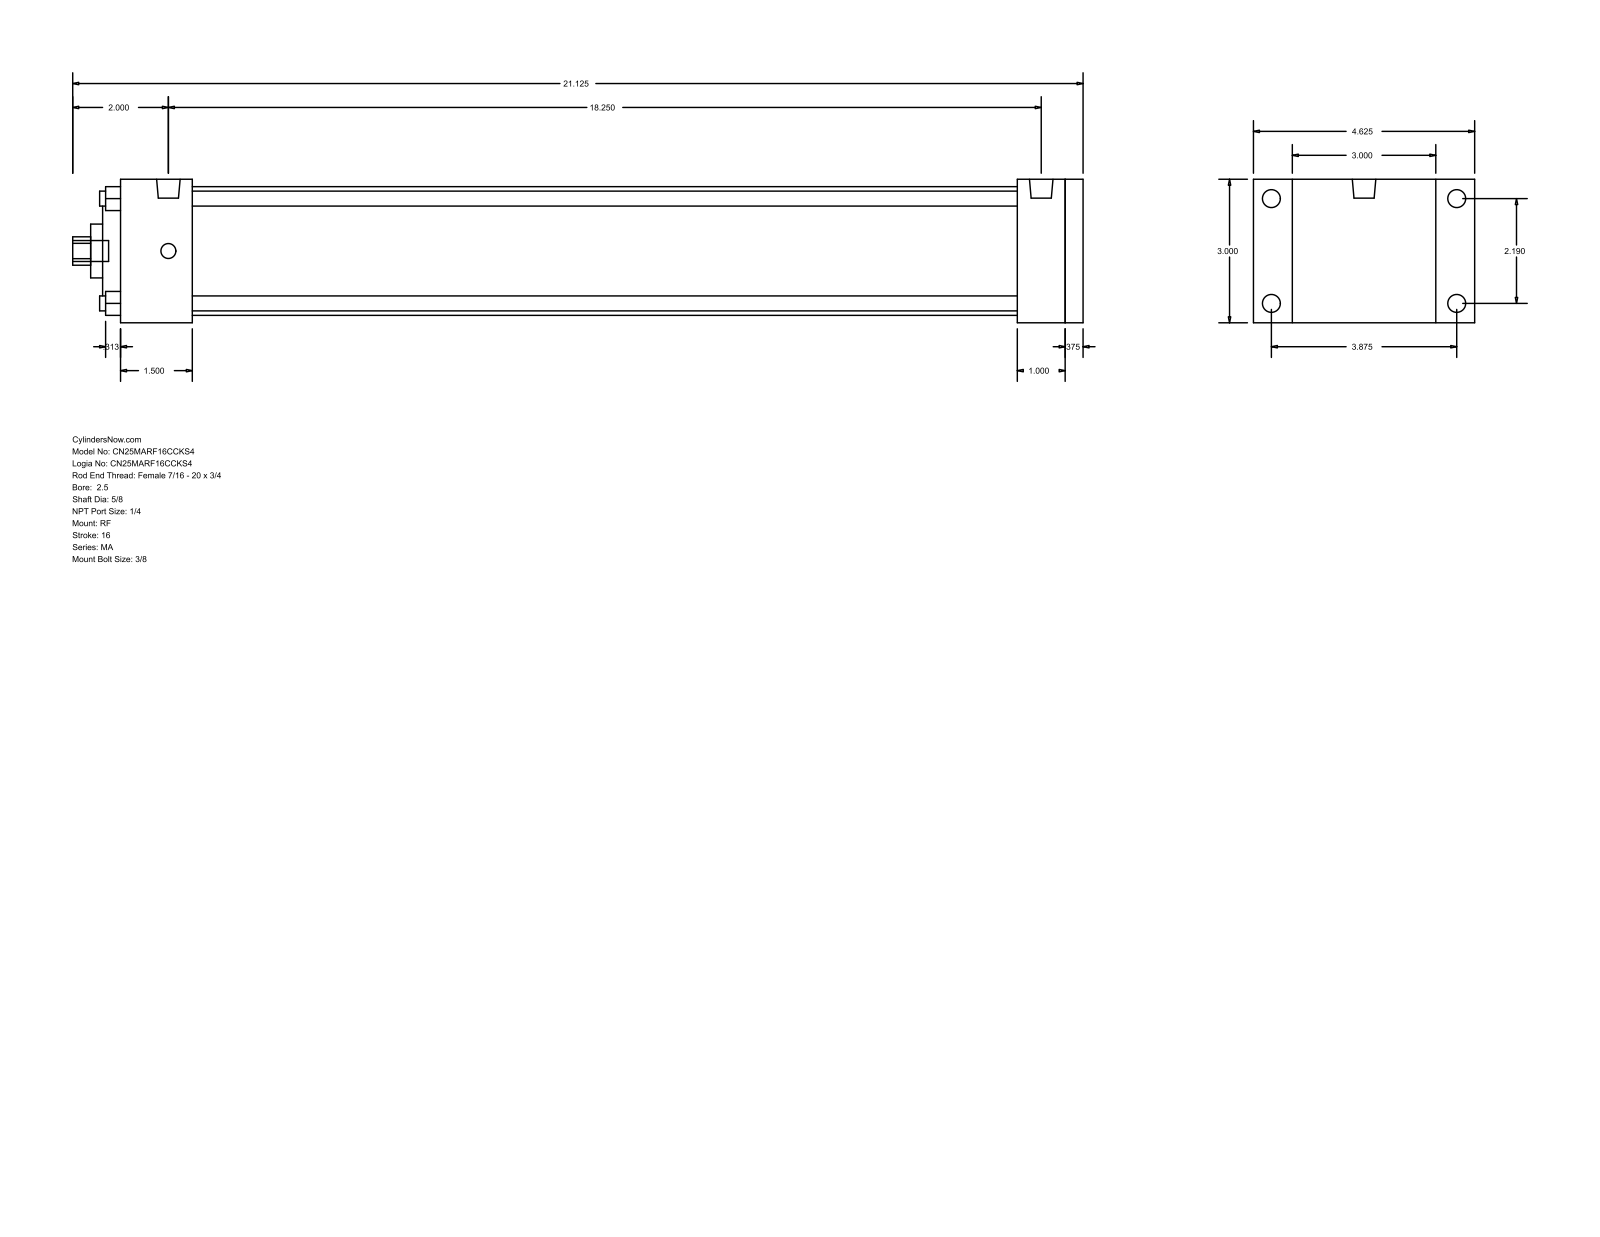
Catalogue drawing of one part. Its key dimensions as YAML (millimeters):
part_name: "MA_RF__0250_0.625"
step_written_by: "GSSL Pune (CONFIG_CONTROL_DESIGN)"
units: millimeters
bodies: {solids: 0, faces: 94, planar: 65, cylindrical: 29, other: 0}
overall_size: [536.58, 117.47, 76.2]
round_holes:
  - {diameter: 7.94, count: 4}
  - {diameter: 15.88, count: 1}
  - {diameter: 28.57, count: 1}
  - {diameter: 50.8, count: 1}
  - {diameter: 68.33, count: 1}
round_bosses_or_shafts:
  - {diameter: 9.53, count: 4}
  - {diameter: 7.94, count: 4}
  - {diameter: 12.49, count: 2}
  - {diameter: 11.11, count: 1}
partial_cylinders:
  - {radius: 7.54, count: 1}
face_to_face_distances: [76.2, 511.18, 9.53, 501.65, 25.4, 38.1, 476.25, 438.15, 463.55, 473.08]
hole_center_spacings: [39.33, 55.62, 78.66]
